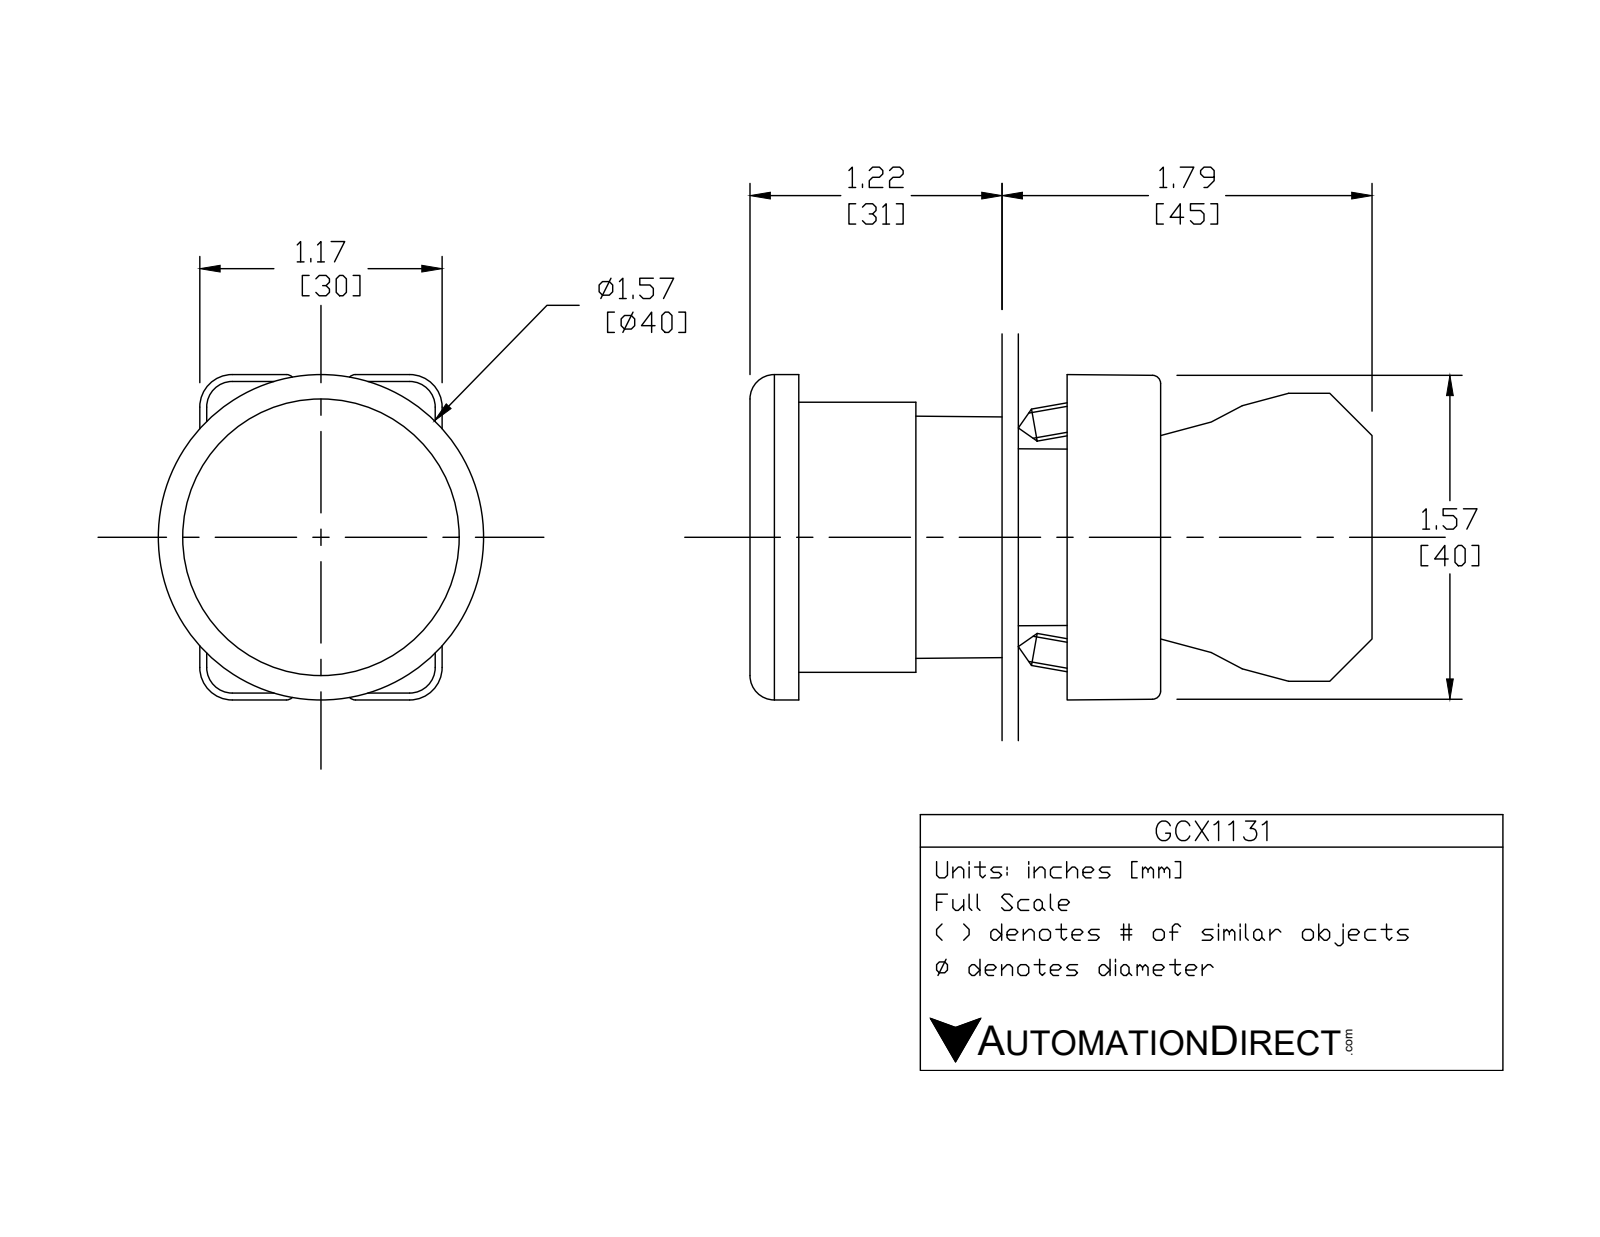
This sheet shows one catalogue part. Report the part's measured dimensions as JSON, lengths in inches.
{"part_name": "GCX1131 OPERATOR; ecx1030; ECX1029-2; GCX1131", "step_written_by": "SolidWorks 2016 (AUTOMOTIVE_DESIGN)", "units": "inches", "bodies": {"solids": 6, "faces": 399, "planar": 230, "cylindrical": 140, "other": 29}, "overall_size": [2.954, 1.581, 1.575], "volume_in3": 1.872, "surface_area_in2": 33.59, "round_holes": [[0.079, 2], [0.124, 2], [0.13, 2], [0.087, 1], [0.197, 1], [0.878, 1], [0.888, 1], [1.024, 1], [1.181, 1]], "round_bosses_or_shafts": [[0.157, 2], [1.575, 1], [1.299, 1], [1.175, 1], [0.945, 1], [0.856, 1], [0.78, 1]], "partial_cylinders_radius": [[0.059, 24], [0.041, 12], [0.124, 12], [0.157, 12], [0.039, 4], [0.128, 2], [0.02, 1], [0.063, 1]], "face_to_face_distances": [1.921, 0.579, 0.033, 1.763, 0.157, 1.724, 0.031, 1.024, 0.76, 1.004], "hole_center_spacings": [0.236, 0.544, 0.472, 0.49]}
